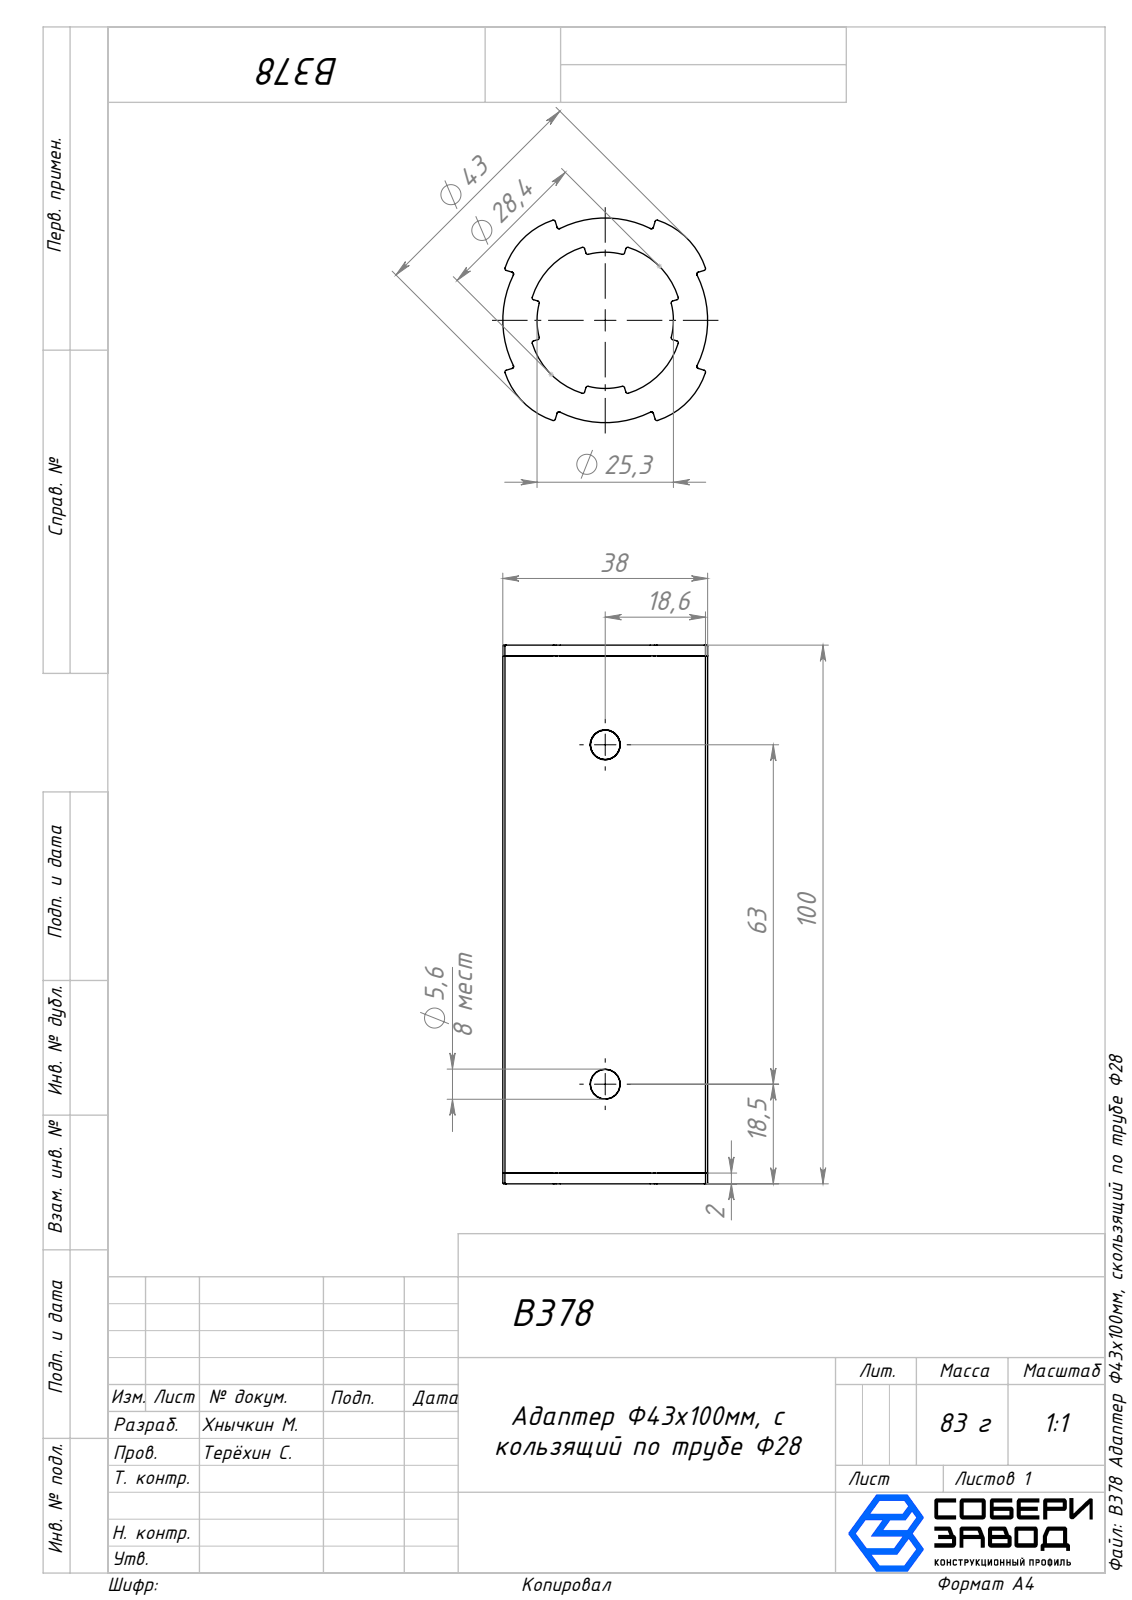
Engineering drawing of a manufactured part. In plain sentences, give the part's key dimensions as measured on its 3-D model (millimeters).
The part is named "Корпус_00; Крышка_00; B378 Адаптер Ф43х100мм, скользящий по трубе Ф28". Its 3-D file was written by "SolidWorks 2025 (AUTOMOTIVE_DESIGN)". It is 3 solids with 686 faces: 176 planar, 370 cylindrical and 140 other. Overall it measures 100 by 38 by 38 millimeters. Its volume is 34 188 cubic millimeters and its surface area 35 061 square millimeters. Round holes: 2 of diameter 5.6, 1 of diameter 30. Partial cylindrical surfaces (rounded edges, fillets, slot ends): 40 of radius 0.35, 36 of radius 0.45, 32 of radius 0.2, 16 of radius 0.4, 12 of radius 1, 4 of radius 14, 3 of radius 16.8, 1 of radius 12.65. The main face-to-face distances are 2, 98, 96, 100, 20.59, 7.08, 87, 13, 11, 85. The hole center spacings are 63.
